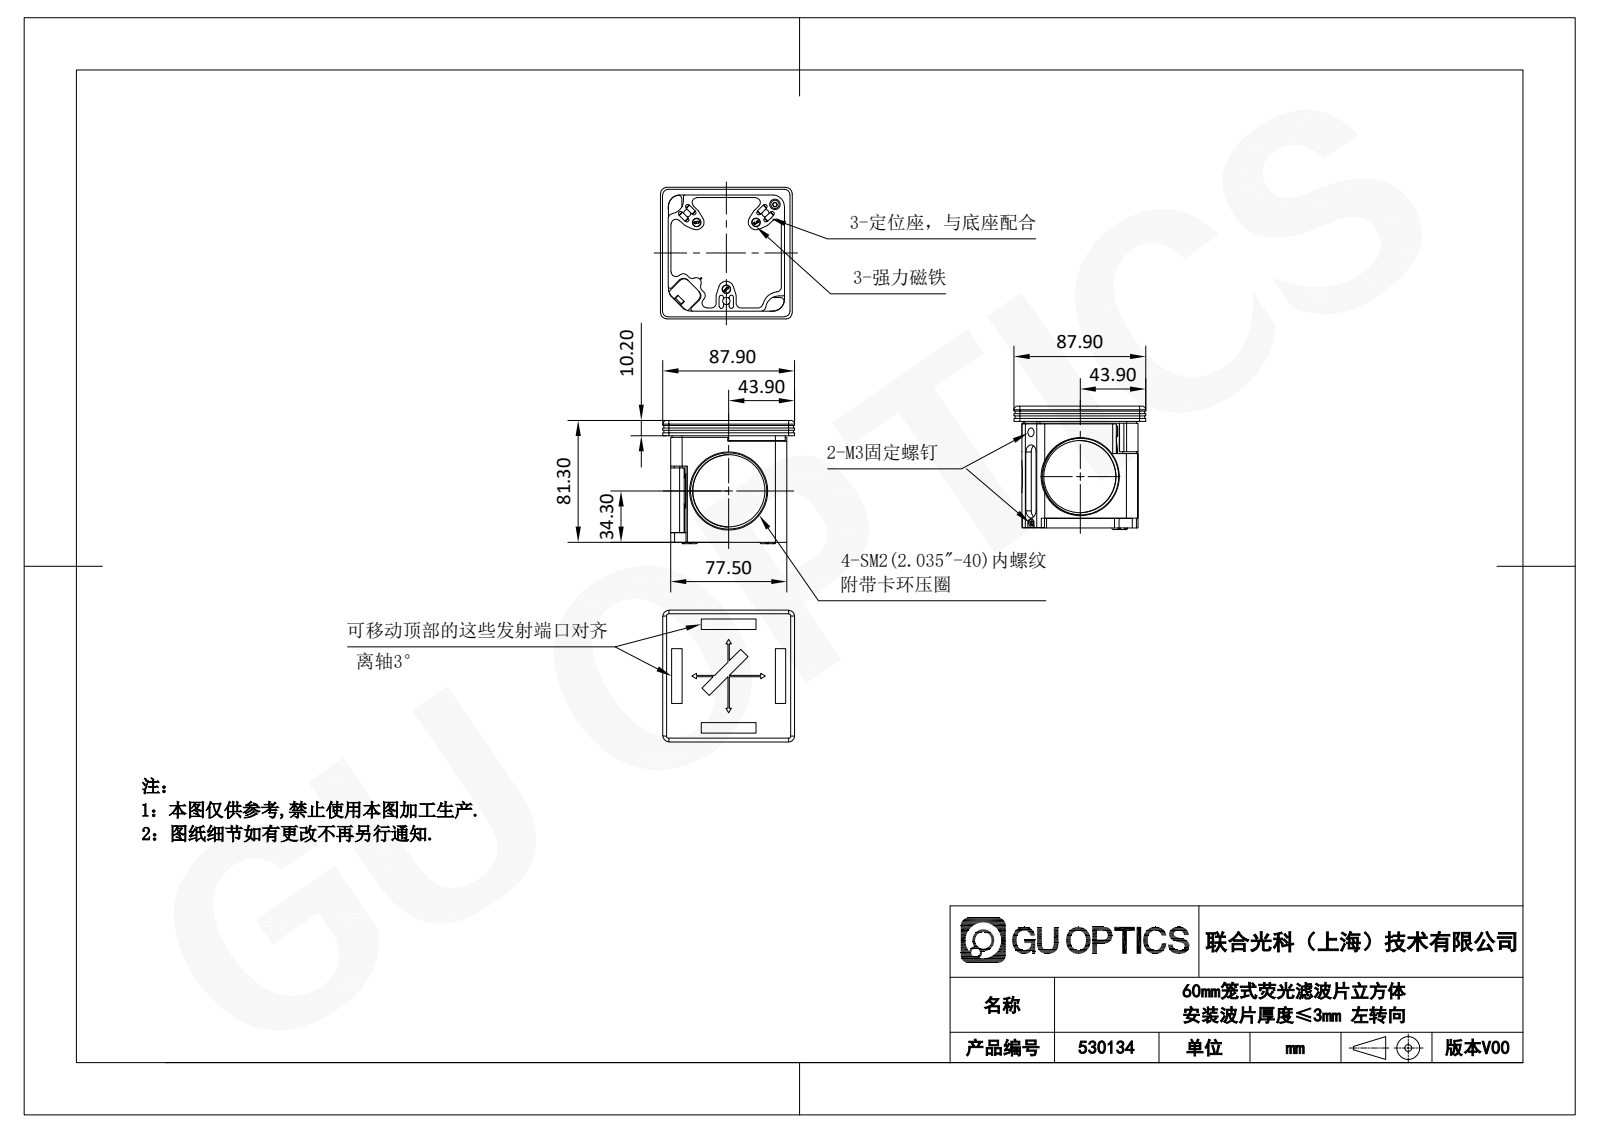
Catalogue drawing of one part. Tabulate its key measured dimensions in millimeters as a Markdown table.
| quantity | value |
| --- | --- |
| part name | 530134 |
| STEP written by | SolidWorks 2020 (CONFIG_CONTROL_DESIGN) |
| units | millimeters |
| bodies | 0 solids, 359 faces (195 planar, 136 cylindrical, 28 other) |
| overall size | 87.9 × 87.9 × 82.3 |
| round holes (diameter × count) | 4.8 × 3, 6 × 3, 7 × 3, 48.3 × 2, 51.1 × 2, 51.17 × 2, 52.1 × 2, 52.17 × 2, 2.5 × 1, 5.8 × 1 |
| round bosses / shafts (diameter × count) | 3 × 4, 5.5 × 1 |
| partial cylindrical surfaces (radius × count) | 3.3 × 21, 1.5 × 12, 2.5 × 8, 3.8 × 8, 3 × 7, 7.6 × 7, 3.2 × 4, 4 × 4 |
| main face-to-face distances | 76.9, 74.8, 2, 11.4, 2.1, 74.9, 77.47, 65.5, 63.5, 63.4 |
| hole center spacings | 8.8, 46.37, 48.73, 55.94, 57.02, 64.06, 66, 7.8 |
